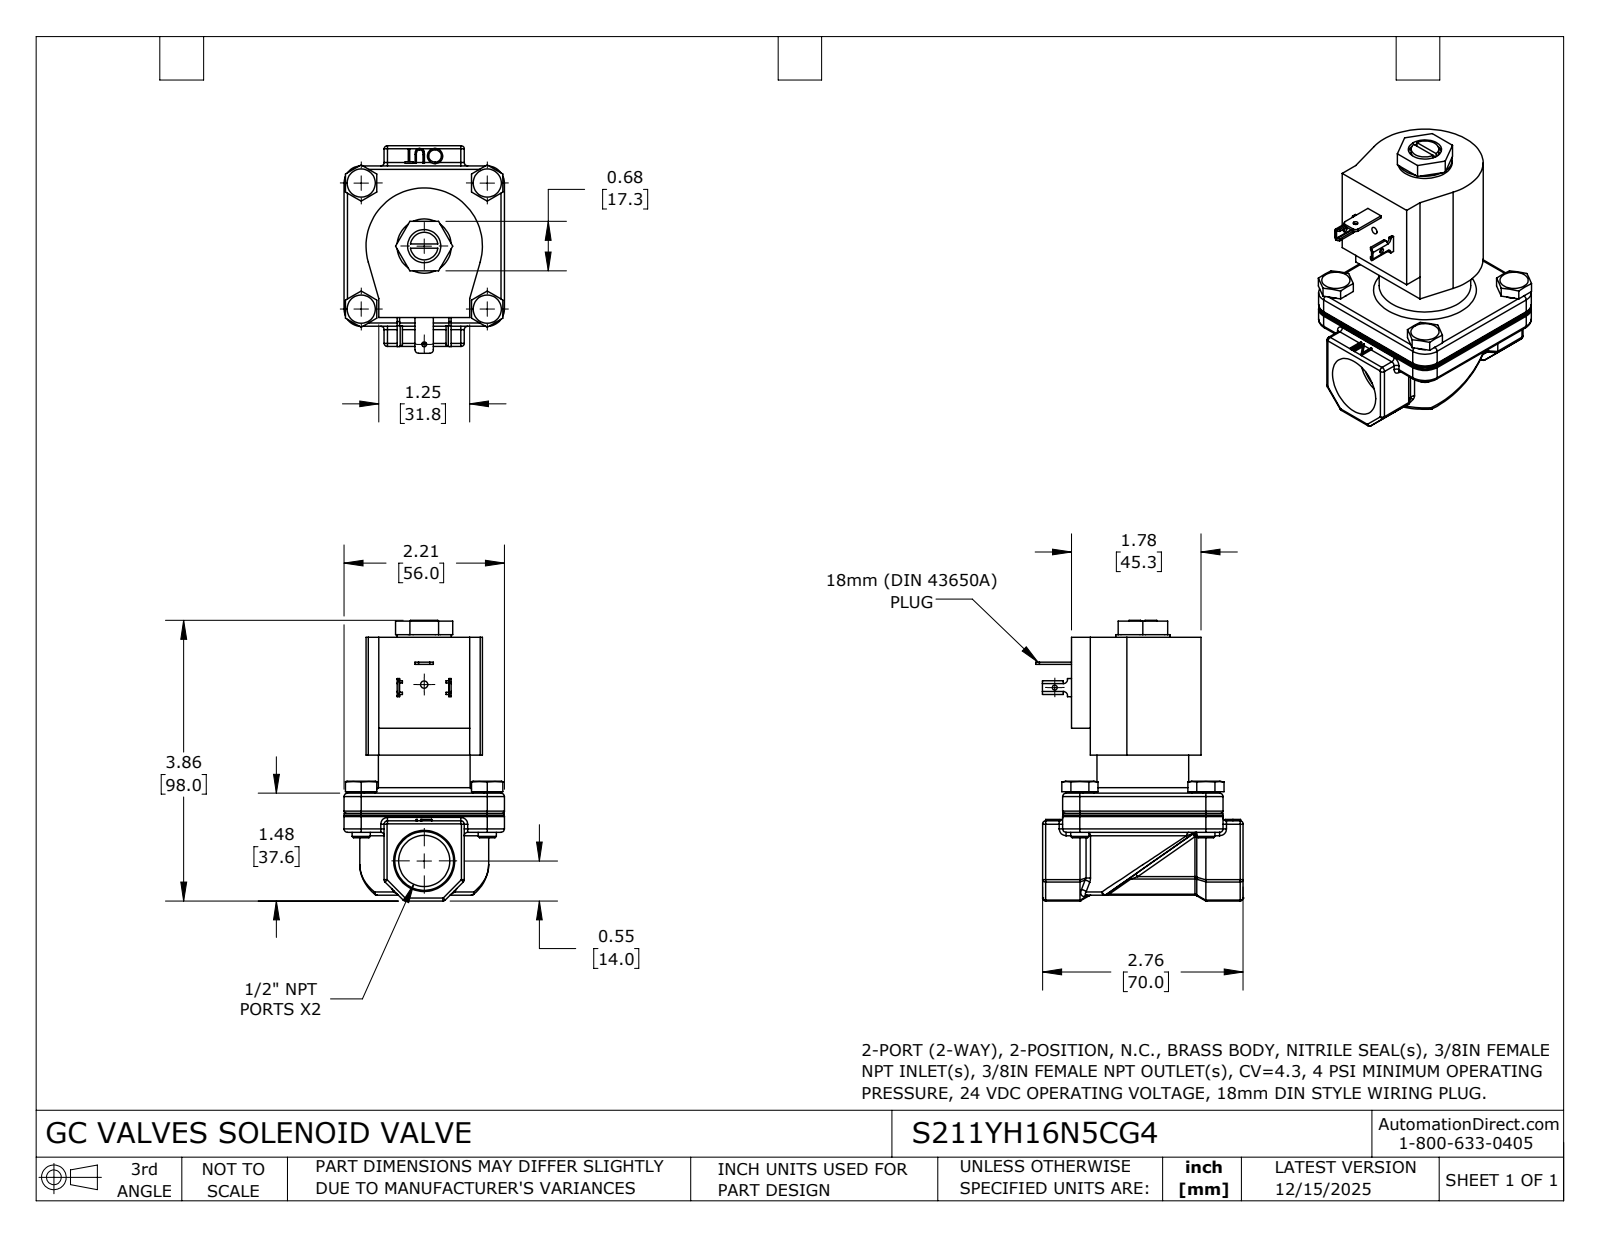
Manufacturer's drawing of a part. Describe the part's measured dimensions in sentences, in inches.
The part is named "S211YH16N5CG4". Its 3-D file was written by "SolidWorks 2024 (CONFIG_CONTROL_DESIGN)". It is 1 solid with 483 faces: 204 planar, 153 cylindrical and 126 other. Overall it measures 3.857 by 2.851 by 2.205 inches. Its volume is 9.336 cubic inches and its surface area 41.74 square inches. Round holes: 1 of diameter 0.066, 1 of diameter 0.067, 1 of diameter 0.1, 1 of diameter 0.456, 1 of diameter 0.703. Round bosses or shafts: 4 of diameter 0.388, 4 of diameter 0.25, 1 of diameter 1.26, 1 of diameter 0.746, 1 of diameter 0.38. Partial cylindrical surfaces (rounded edges, fillets, slot ends): 57 of radius 0.047, 12 of radius 0.04, 4 of radius 0.006, 4 of radius 0.031, 4 of radius 0.041, 4 of radius 0.234, 4 of radius 0.236, 2 of radius 0.05. The main face-to-face distances are 2.143, 0.551, 1.654, 2.205, 0.537, 2.68, 0.276, 2.48, 1.06, 0.523. The hole center spacings are 1.35, 2.423.
